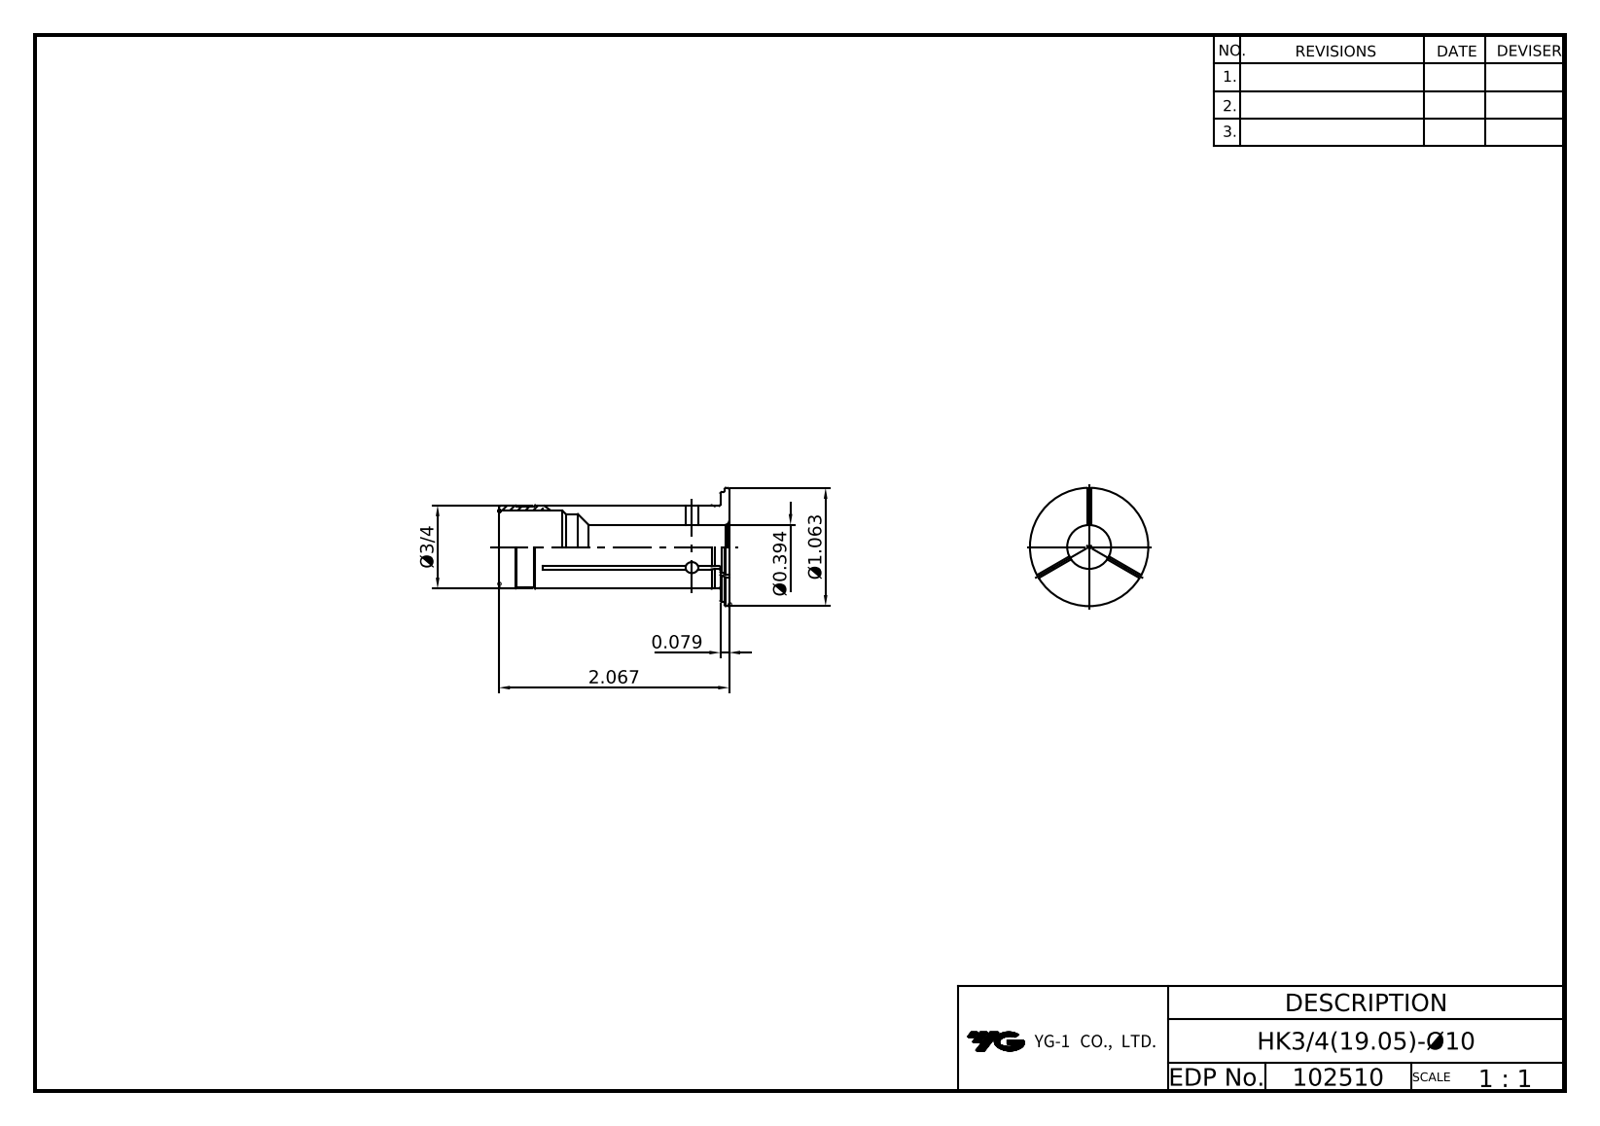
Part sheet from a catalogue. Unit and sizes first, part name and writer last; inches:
Units: inches
Overall size (bounding box): 2.067 × 1.063 × 1.063
Round holes (diameter × count): ⌀0.394 ×1, ⌀0.591 ×1, ⌀0.65 ×1
Round bosses / shafts (diameter × count): ⌀1.063 ×1, ⌀0.984 ×1, ⌀0.75 ×1
Main face-to-face distances: 0.079, 0.039, 1.988, 2.028, 2.067
Volume: 0.543 in³ · Surface area: 9.48 in²
Bodies: 1 solid, 12 faces (4 planar, 6 cylindrical, 2 other)
Part name (STEP PRODUCT): LO-HK19.05-10
STEP written by: Autodesk Inventor 2025 (AP242_MANAGED_MODEL_BASED_3D_ENGINEERING_MIM_LF)
